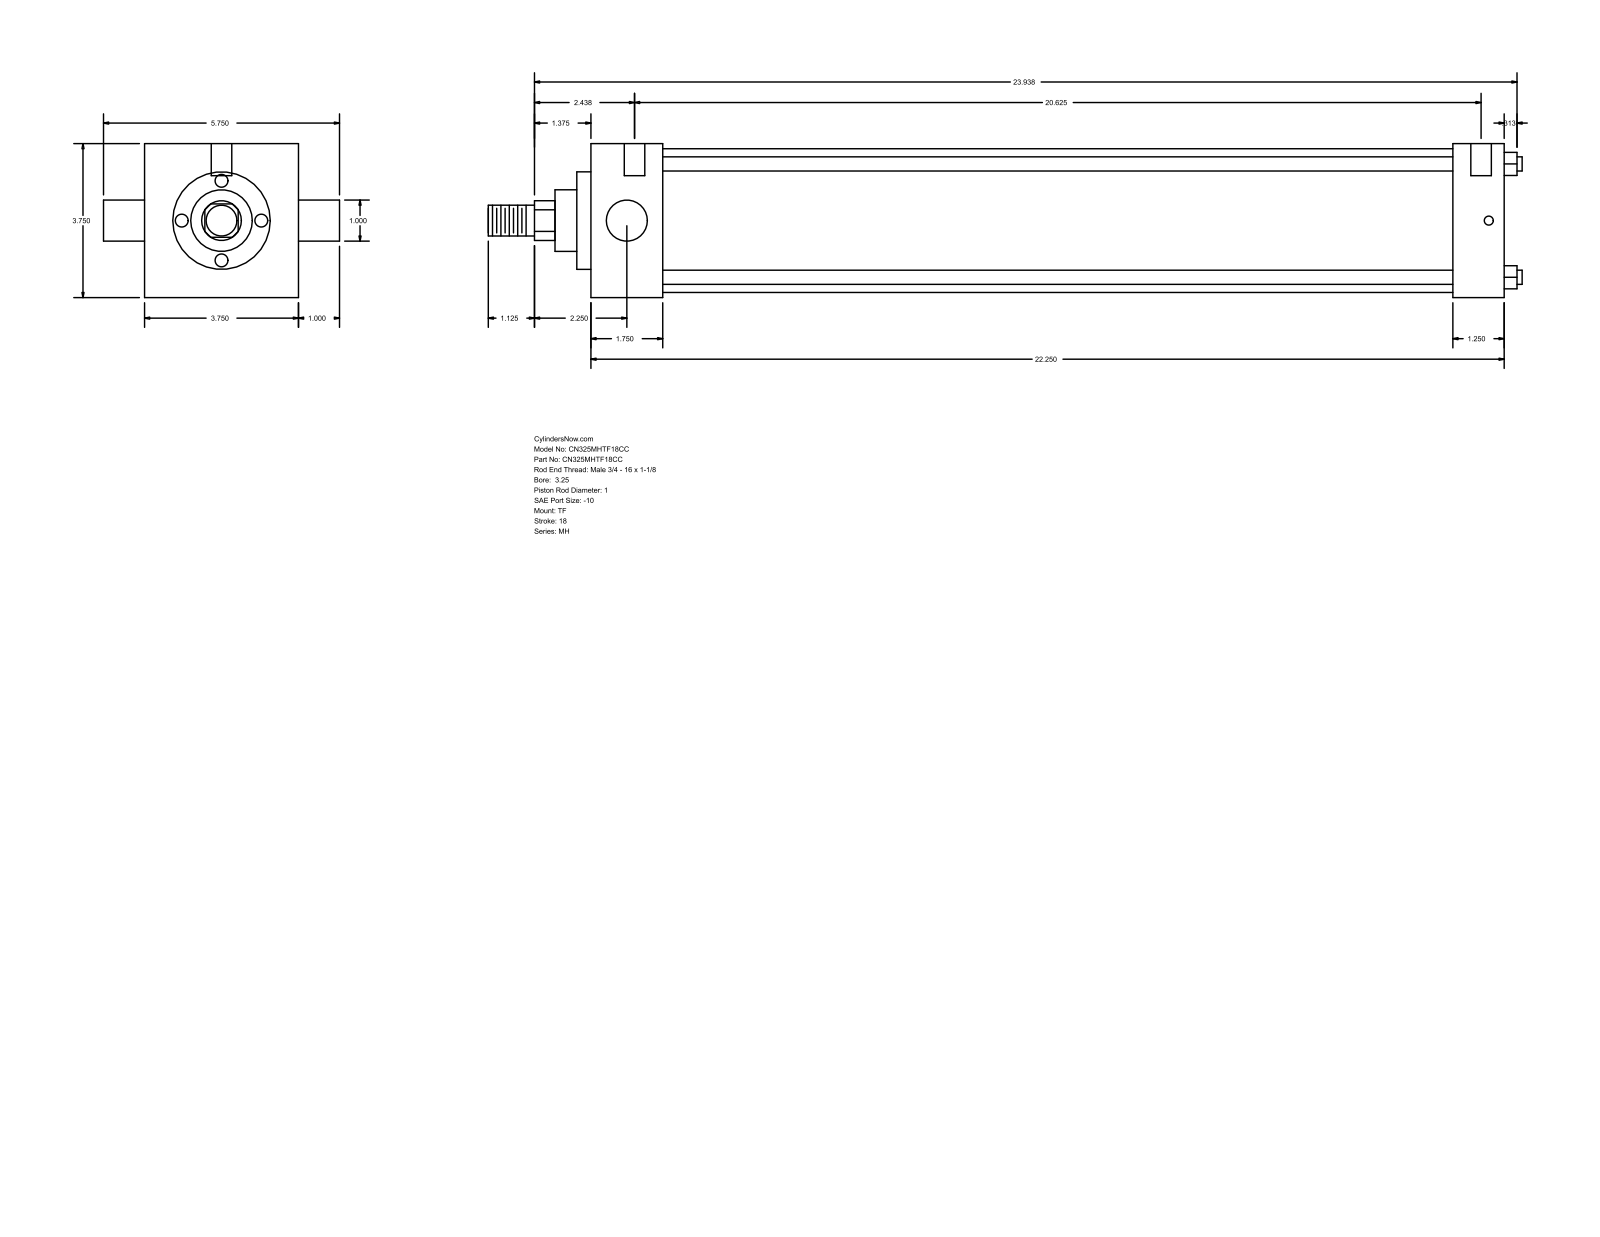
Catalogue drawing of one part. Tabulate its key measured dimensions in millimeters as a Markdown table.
| quantity | value |
| --- | --- |
| part name | MH_TF__0325_1 |
| STEP written by | GSSL Pune (CONFIG_CONTROL_DESIGN) |
| units | millimeters |
| bodies | 0 solids, 86 faces (61 planar, 25 cylindrical, 0 other) |
| overall size | 639.76 × 146.05 × 95.25 |
| round holes (diameter × count) | 5.56 × 3, 12.7 × 2 |
| round bosses / shafts (diameter × count) | 8.76 × 4, 25.4 × 2, 88.9 × 1, 60.33 × 1, 38.1 × 1, 19.05 × 1 |
| partial cylindrical surfaces (radius × count) | 12.29 × 1 |
| main face-to-face distances | 95.24, 565.16, 44.46, 533.41, 488.95, 520.7, 31.75, 8.73, 53.19, 542.14 |
| hole center spacings | 1.58, 4.76, 523.88, 525.46, 528.64, 530.22 |
